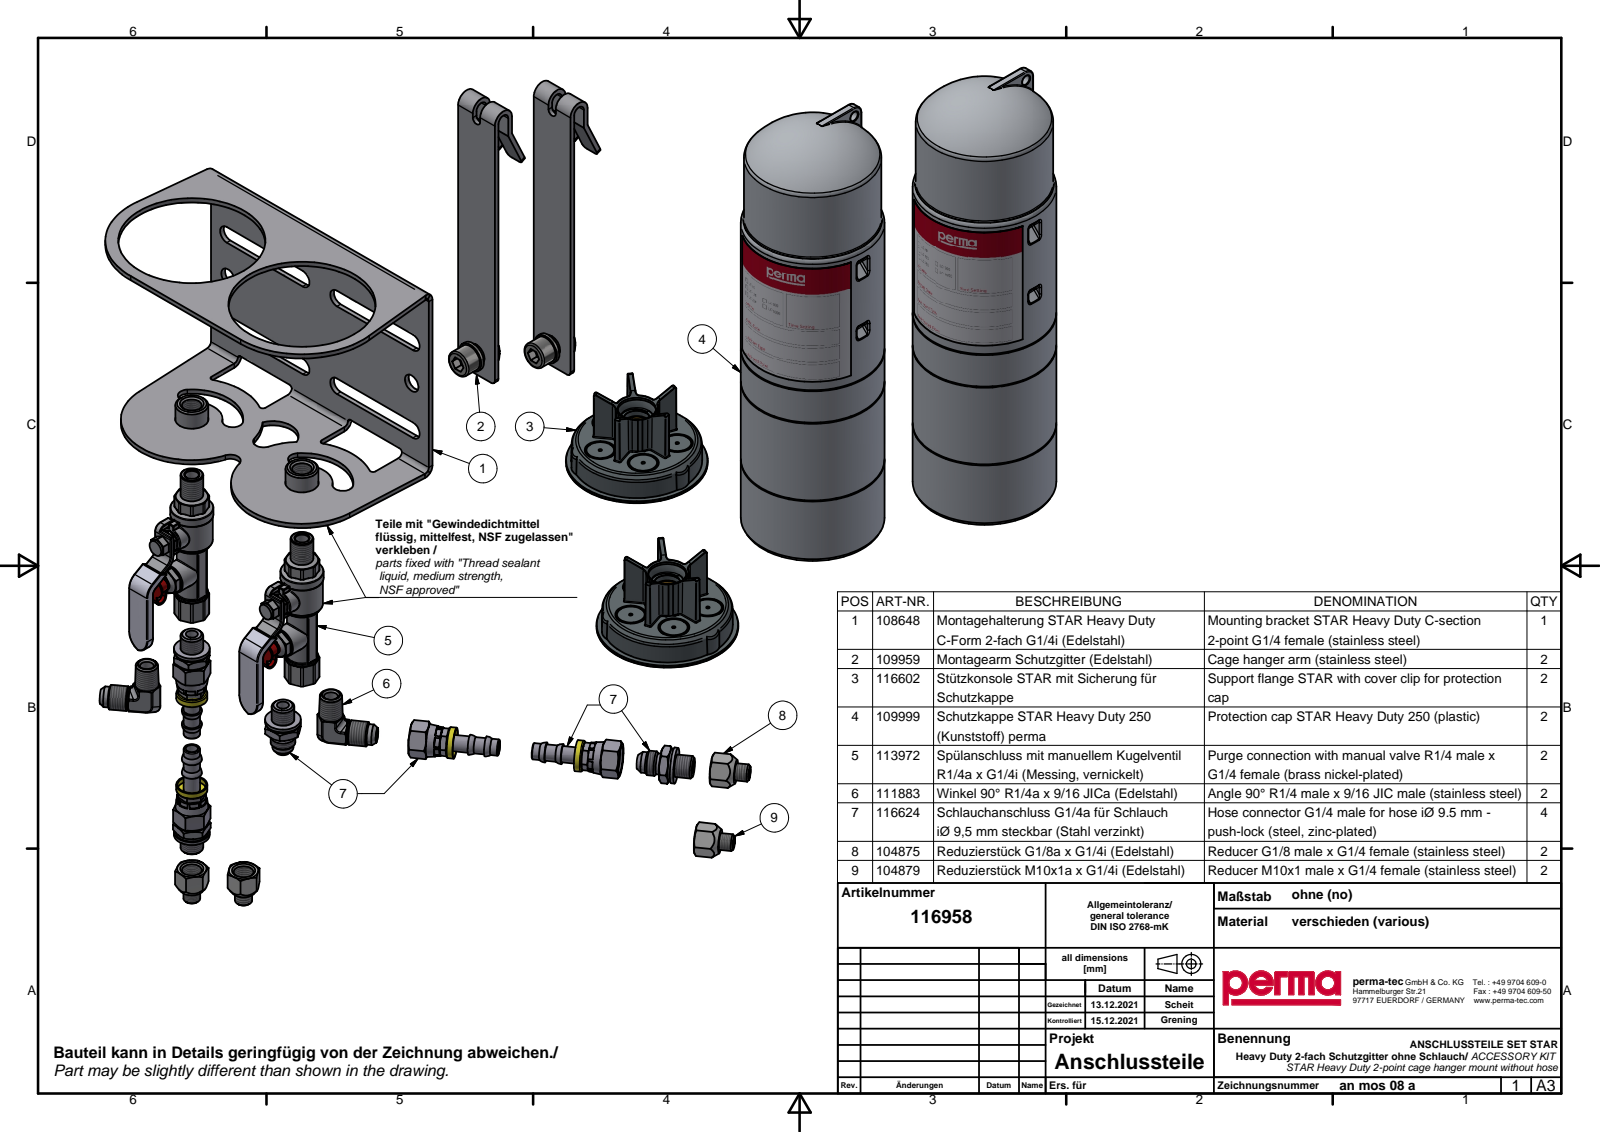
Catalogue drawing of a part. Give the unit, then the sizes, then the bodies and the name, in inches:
Units: inches
Overall size (bounding box): 20.887 × 12.126 × 5.439
Round holes (diameter × count): ⌀0.709 ×10, ⌀0.236 ×5, ⌀0.451 ×5, ⌀0.433 ×4, ⌀0.276 ×3, ⌀0.315 ×3, ⌀0.075 ×2, ⌀0.079 ×2, ⌀0.197 ×2, ⌀0.22 ×2, ⌀0.33 ×2, ⌀0.394 ×2
Round bosses / shafts (diameter × count): ⌀0.433 ×4, ⌀0.374 ×4, ⌀0.315 ×4, ⌀0.394 ×3, ⌀3.268 ×2, ⌀3.228 ×2, ⌀3.126 ×2, ⌀0.984 ×2
Partial cylindrical surfaces — rounded edges, fillets, slot ends (radius × count): R0.02 ×163, R0.039 ×29, R0.016 ×24, R0.079 ×24, R0.012 ×20, R0.118 ×19, R0.394 ×10, R0.449 ×10
Main face-to-face distances: 0.118, 4.969, 0.236, 5.087, 4.851, 0.642, 4.327, 0.76, 4.209, 0.669
Hole centre spacings: 0.933, 1.775, 3.543, 1.097, 1.096, 0.984, 1.285, 1.935
Volume: 48.92 in³ · Surface area: 829.7 in²
Bodies: 41 solids, 3181 faces (852 planar, 667 cylindrical, 1662 other)
Part name (STEP PRODUCT): anmos08a_CI Modell; anmha04c; Hülse G1_4; Schweißnaht (+8 more)
STEP written by: Autodesk Inventor 2022 (CONFIG_CONTROL_DESIGN)
